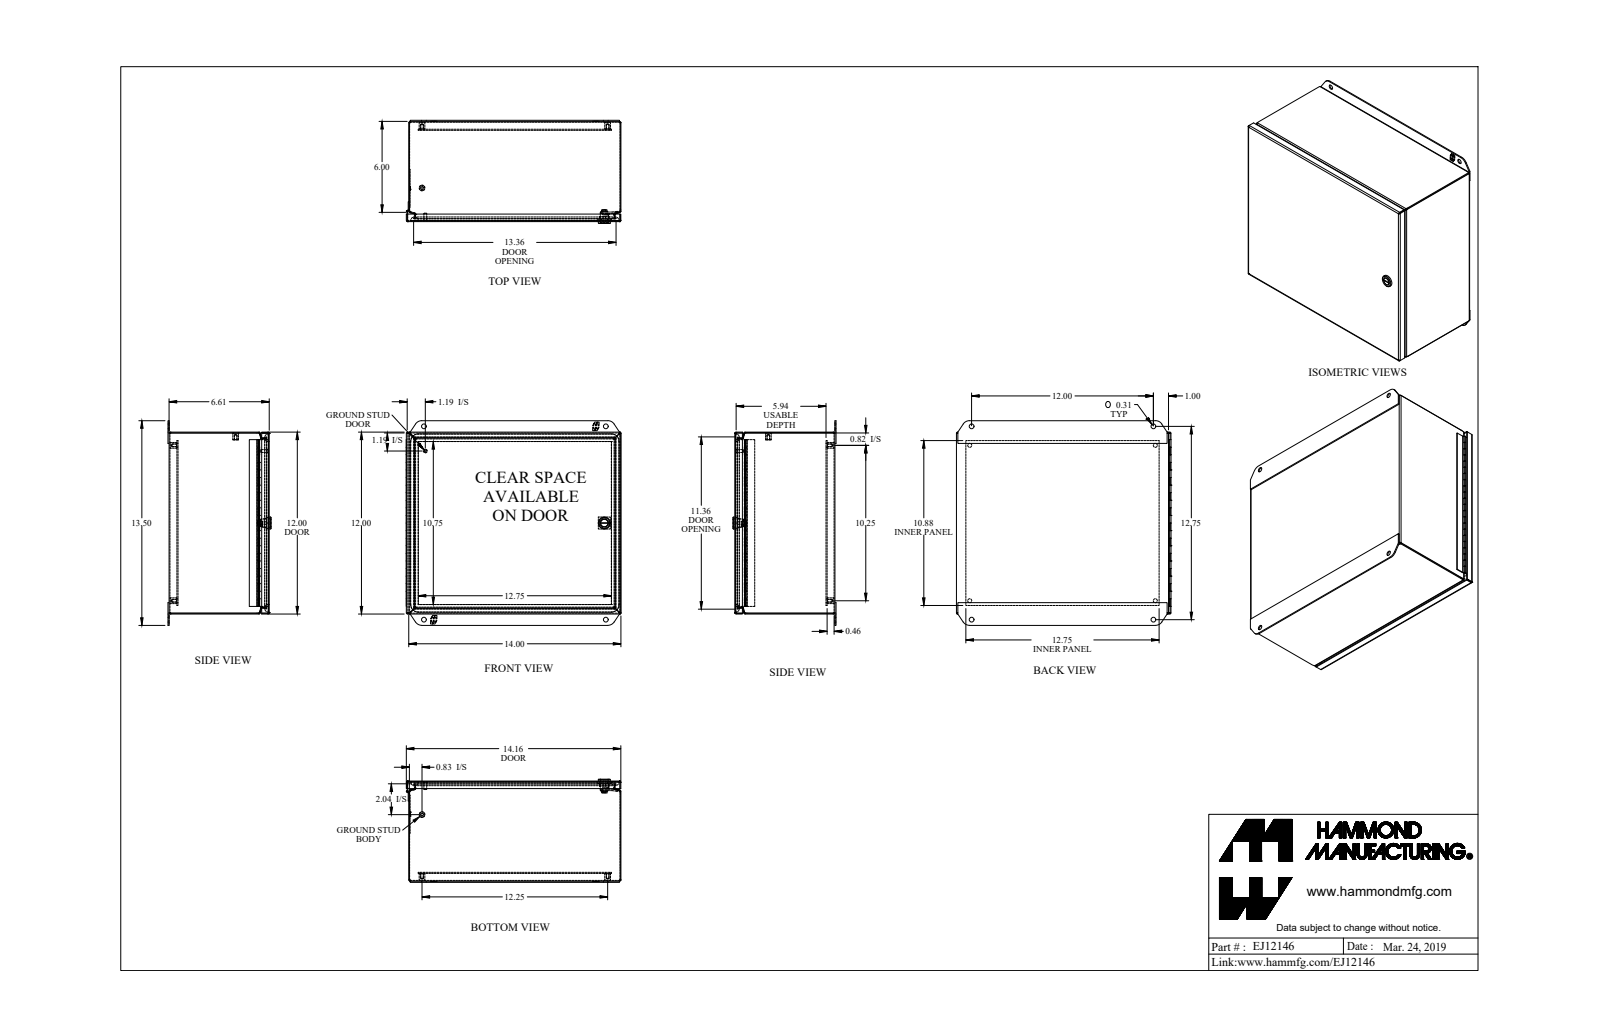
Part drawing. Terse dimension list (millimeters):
name: EJ12146_Default
written by: SolidWorks 2019 (CONFIG_CONTROL_DESIGN)
unit: mm
bodies: 16 solids, 707 faces (393 planar, 222 cylindrical, 92 other)
size: 359.8 × 342.9 × 172.8
volume: 959 300 mm³; area: 1 245 000 mm²
holes: 5× ⌀4, 4× ⌀6.7, 4× ⌀8, 1× ⌀1.3, 1× ⌀13.1
bosses: 5× ⌀9.5, 1× ⌀20, 1× ⌀13.6, 1× ⌀12.6, 1× ⌀11, 1× ⌀6.4, 1× ⌀4.8, 1× ⌀2.5
rounds: 16× R0.7, 16× R2.2, 10× R7.1, 4× R6.4, 4× R12.7, 4× R12.7, 2× R1.5, 2× R13.7
face distances: 1.4, 166.5, 1.8, 15, 303.4, 167.9, 165, 354.2, 11.7, 13.1
hole spacings: 424.5, 31.9, 292.1, 309.6, 405.7, 260.4, 260.4, 311.2
